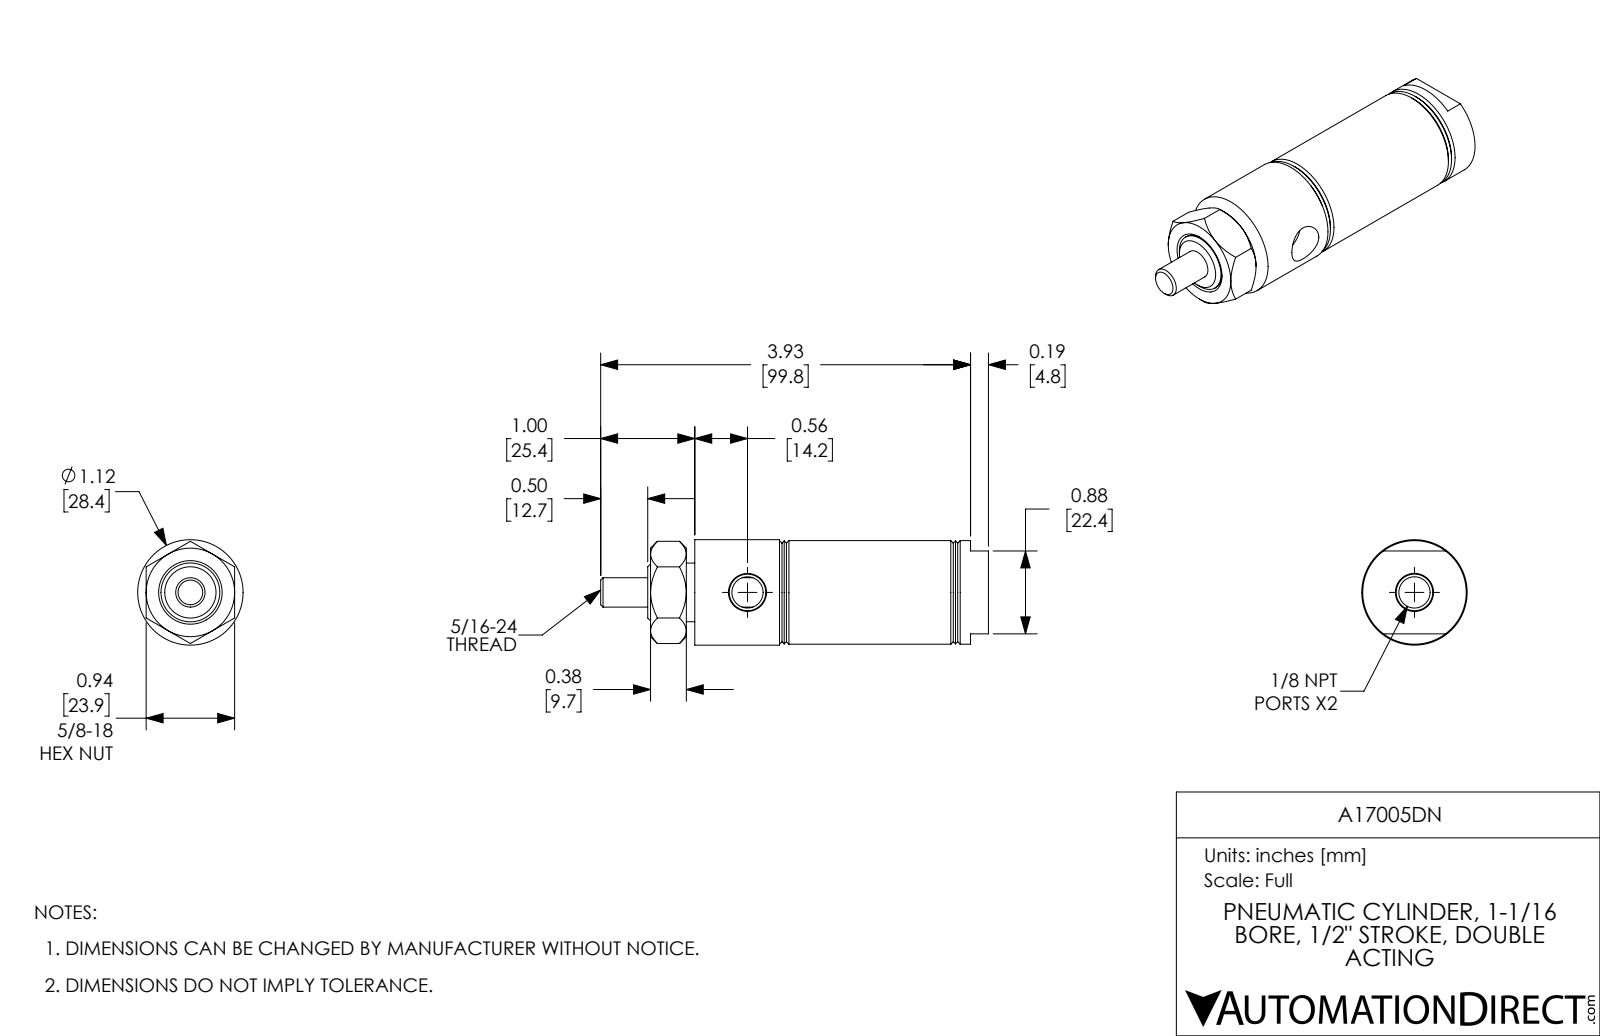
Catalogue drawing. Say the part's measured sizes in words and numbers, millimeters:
The part is named "A17005DN; A17005DN_Mounting Nut_D-9; A17005DN-Rod; A17005DN-MainBody". Its 3-D file was written by "SolidWorks 2017 (AUTOMOTIVE_DESIGN)". It is 3 solids with 94 faces: 24 planar, 26 cylindrical and 44 other. Overall it measures 104.6 by 28.4 by 28.4 millimeters. Its volume is 45 720 cubic millimeters and its surface area 19 610 square millimeters. Round holes: 2 of diameter 8.4, 1 of diameter 7.9, 1 of diameter 15.9, 1 of diameter 27. Round bosses or shafts: 1 of diameter 28.4, 1 of diameter 27.9, 1 of diameter 15.9, 1 of diameter 15.8. The main face-to-face distances are 12.7, 52.3, 25.4, 39.6, 26.9, 39.6, 52.3, 79.2, 26.9, 23.9.
